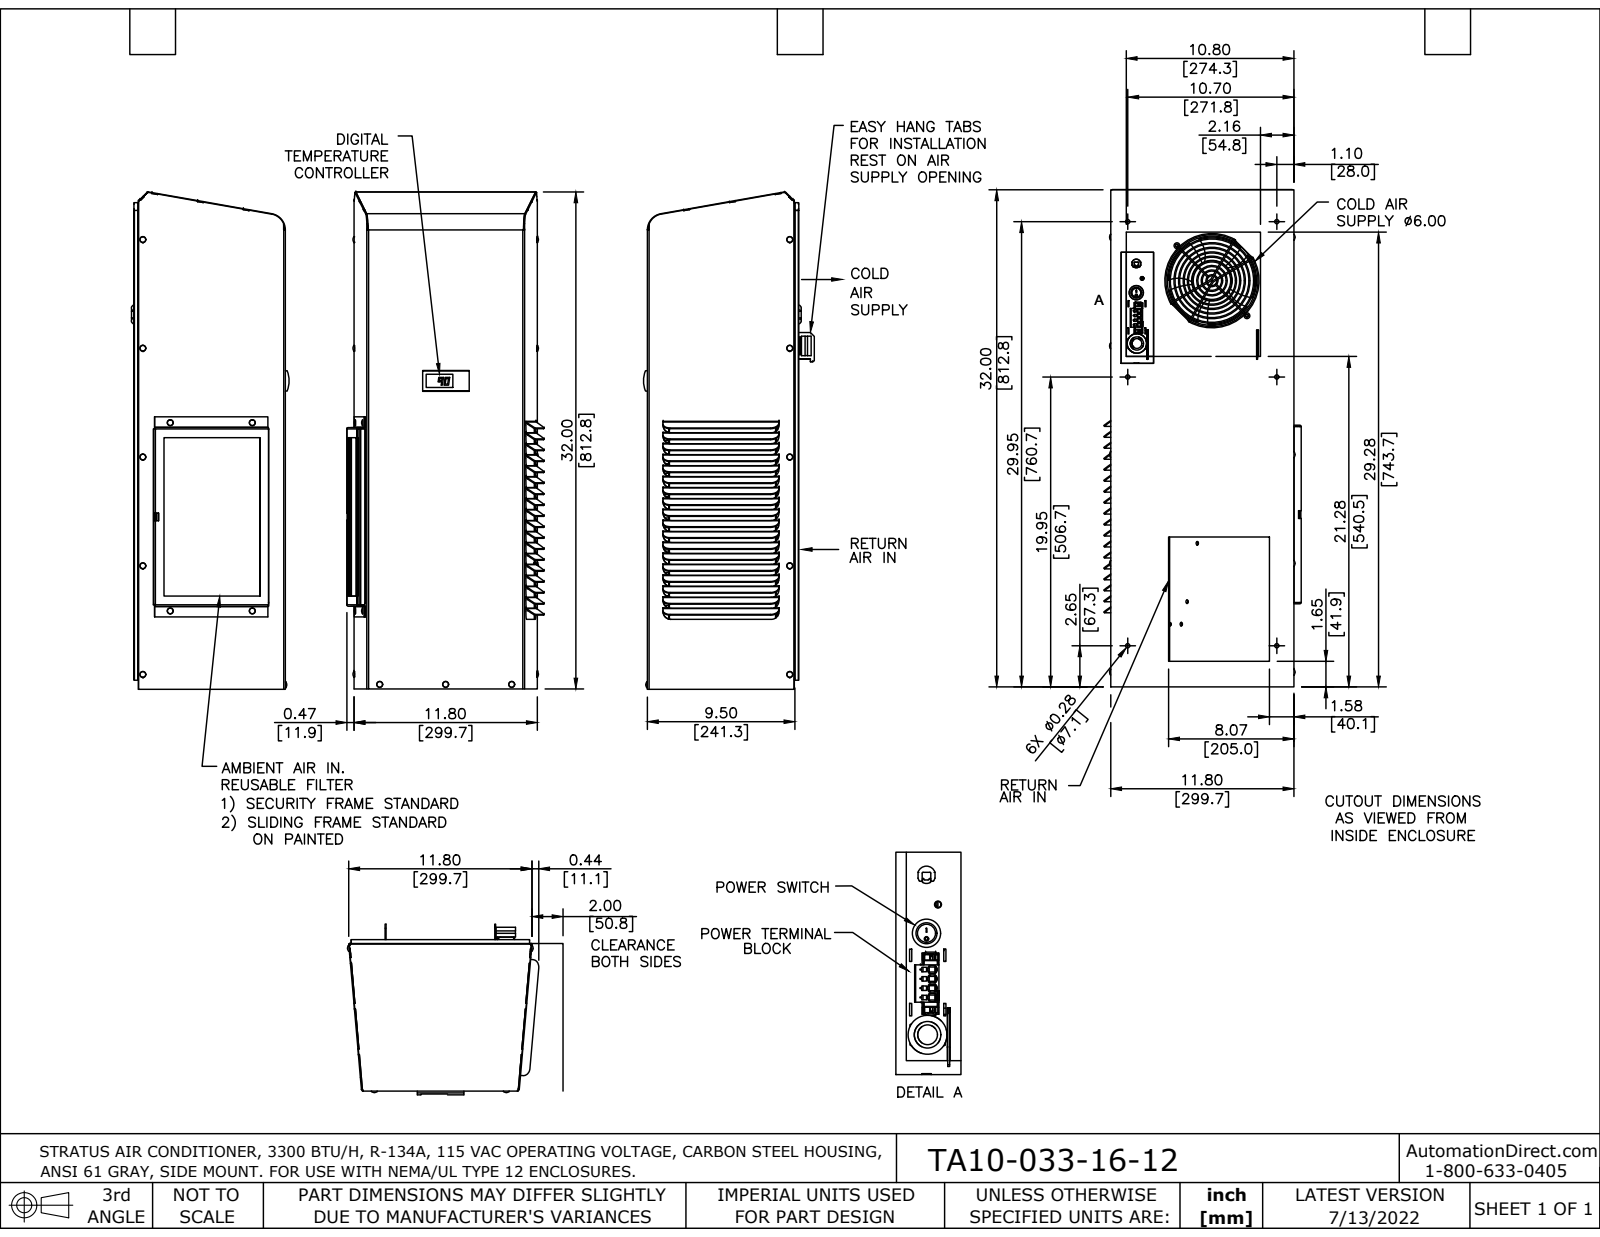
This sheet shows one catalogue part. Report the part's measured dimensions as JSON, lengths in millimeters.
{"part_name": "TA10-033-16-12", "step_written_by": "SolidWorks 2021 (AUTOMOTIVE_DESIGN)", "units": "millimeters", "bodies": {"solids": 1, "faces": 1736, "planar": 1073, "cylindrical": 493, "other": 170}, "overall_size": [813.4, 319.4, 293.5], "volume_mm3": 2237000, "surface_area_mm2": 2063000, "round_holes": [[4, 11], [5.2, 5], [152.4, 1]], "round_bosses_or_shafts": [[4.8, 7], [9, 2], [6.3, 2], [154.2, 1], [23, 1], [9.9, 1], [9.6, 1], [2.2, 1]], "partial_cylinders_radius": [[0.4, 45], [0.3, 42], [12.7, 36], [12.9, 36], [2.5, 28], [1.5, 21], [2.9, 21], [0.8, 13]], "face_to_face_distances": [1.5, 238.2, 239.6, 1.4, 239.5, 241, 1.5, 9.5, 6.5, 7.8], "hole_center_spacings": [177.8, 355.6, 533.4, 134.6, 166.8, 307.8, 44, 44]}
